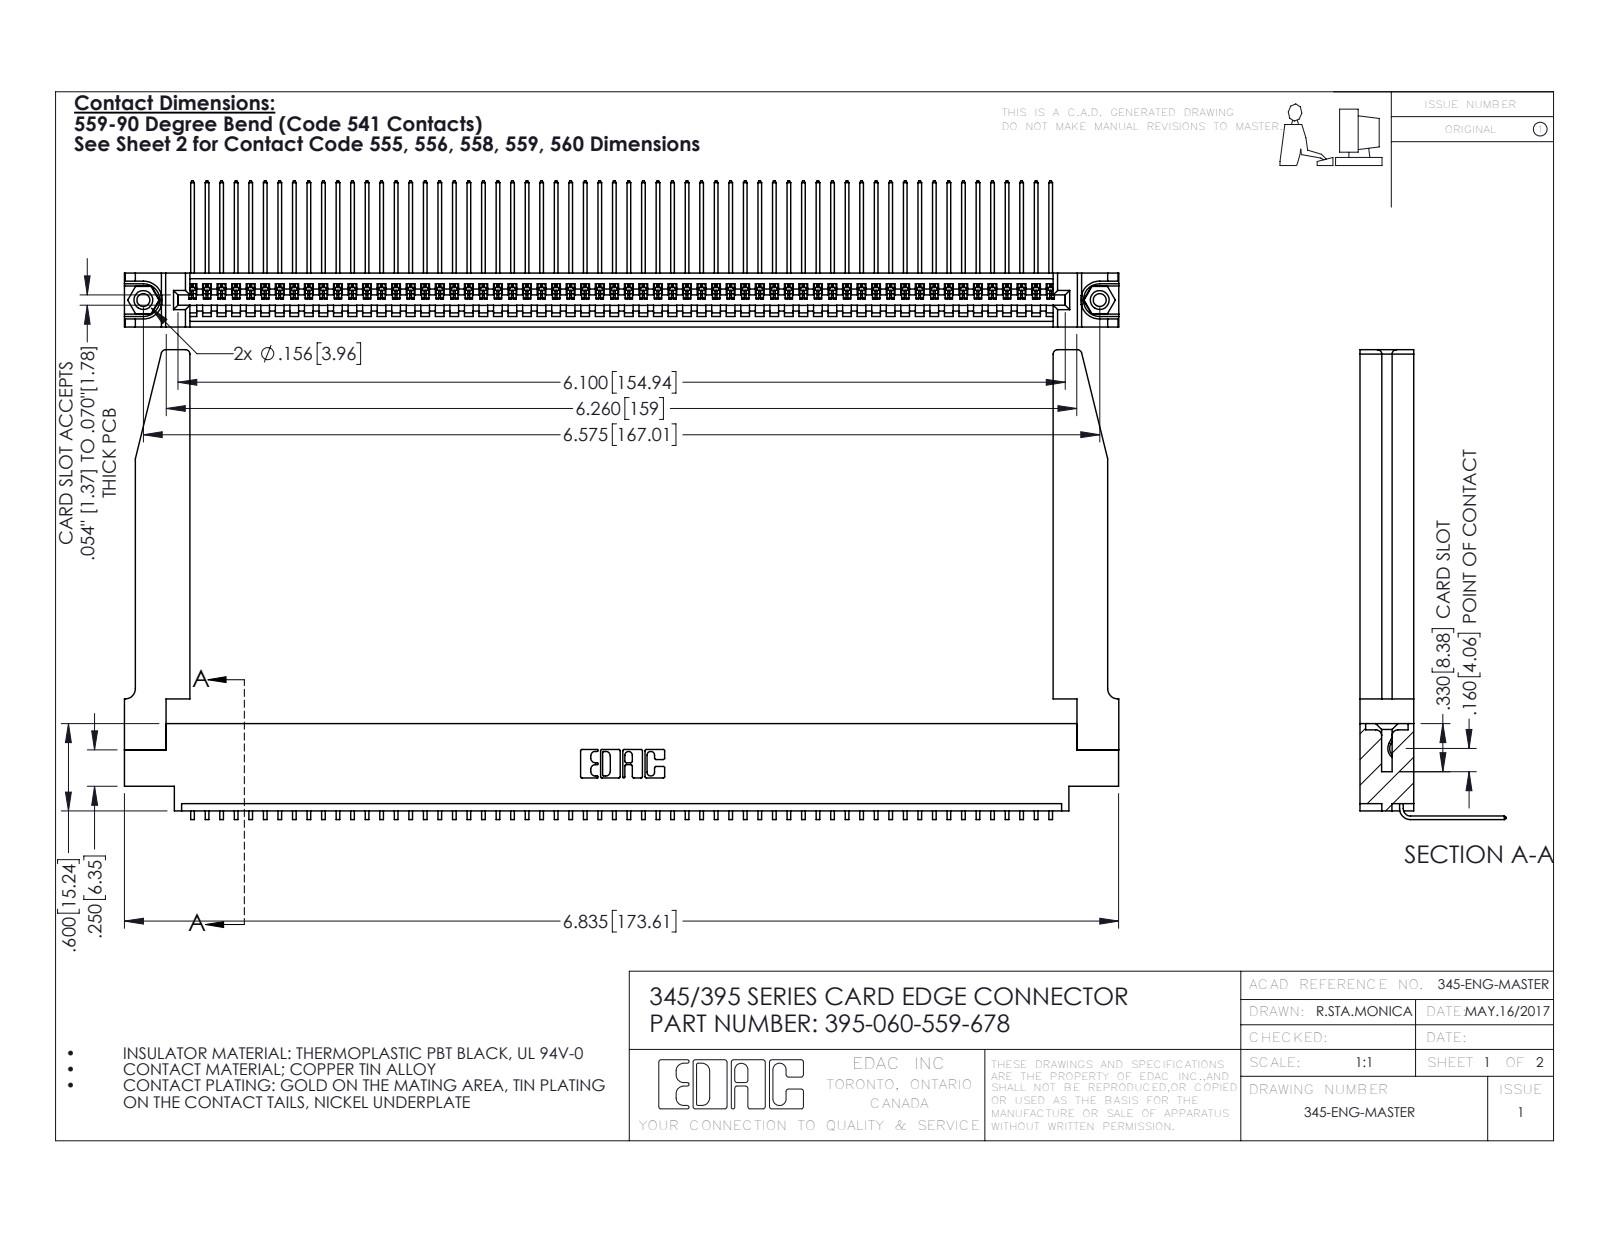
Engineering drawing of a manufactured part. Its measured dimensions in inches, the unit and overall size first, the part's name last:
Units: inches
Overall size (bounding box): 6.836 × 3.229 × 1.005
Round holes (diameter × count): ⌀0.089 ×2, ⌀0.125 ×2, ⌀0.156 ×2, ⌀0.064 ×1
Round bosses / shafts (diameter × count): ⌀0.155 ×2
Partial cylindrical surfaces — rounded edges, fillets, slot ends (radius × count): R0.006 ×120, R0.01 ×22, R0.03 ×8, R0.007 ×6, R0.031 ×6, R0.026 ×3, R0.031 ×2, R0.04 ×2
Main face-to-face distances: 0.37, 0.072, 0.298, 0.098, 0.272, 0.025, 0.2, 0.225, 0.148, 0.15
Hole centre spacings: 0.27, 6.339, 6.575
Volume: 1.495 in³ · Surface area: 47.46 in²
Bodies: 65 solids, 3964 faces (2746 planar, 1166 cylindrical, 52 other)
Part name (STEP PRODUCT): 345 Part_0.170 Offset - 0.156 Dia-TH; 345-250-001_345-250-001-102; 395-060-559-678; 345-220-078_345-220-078 (+1 more)
STEP written by: SolidWorks 2016 (CONFIG_CONTROL_DESIGN)
